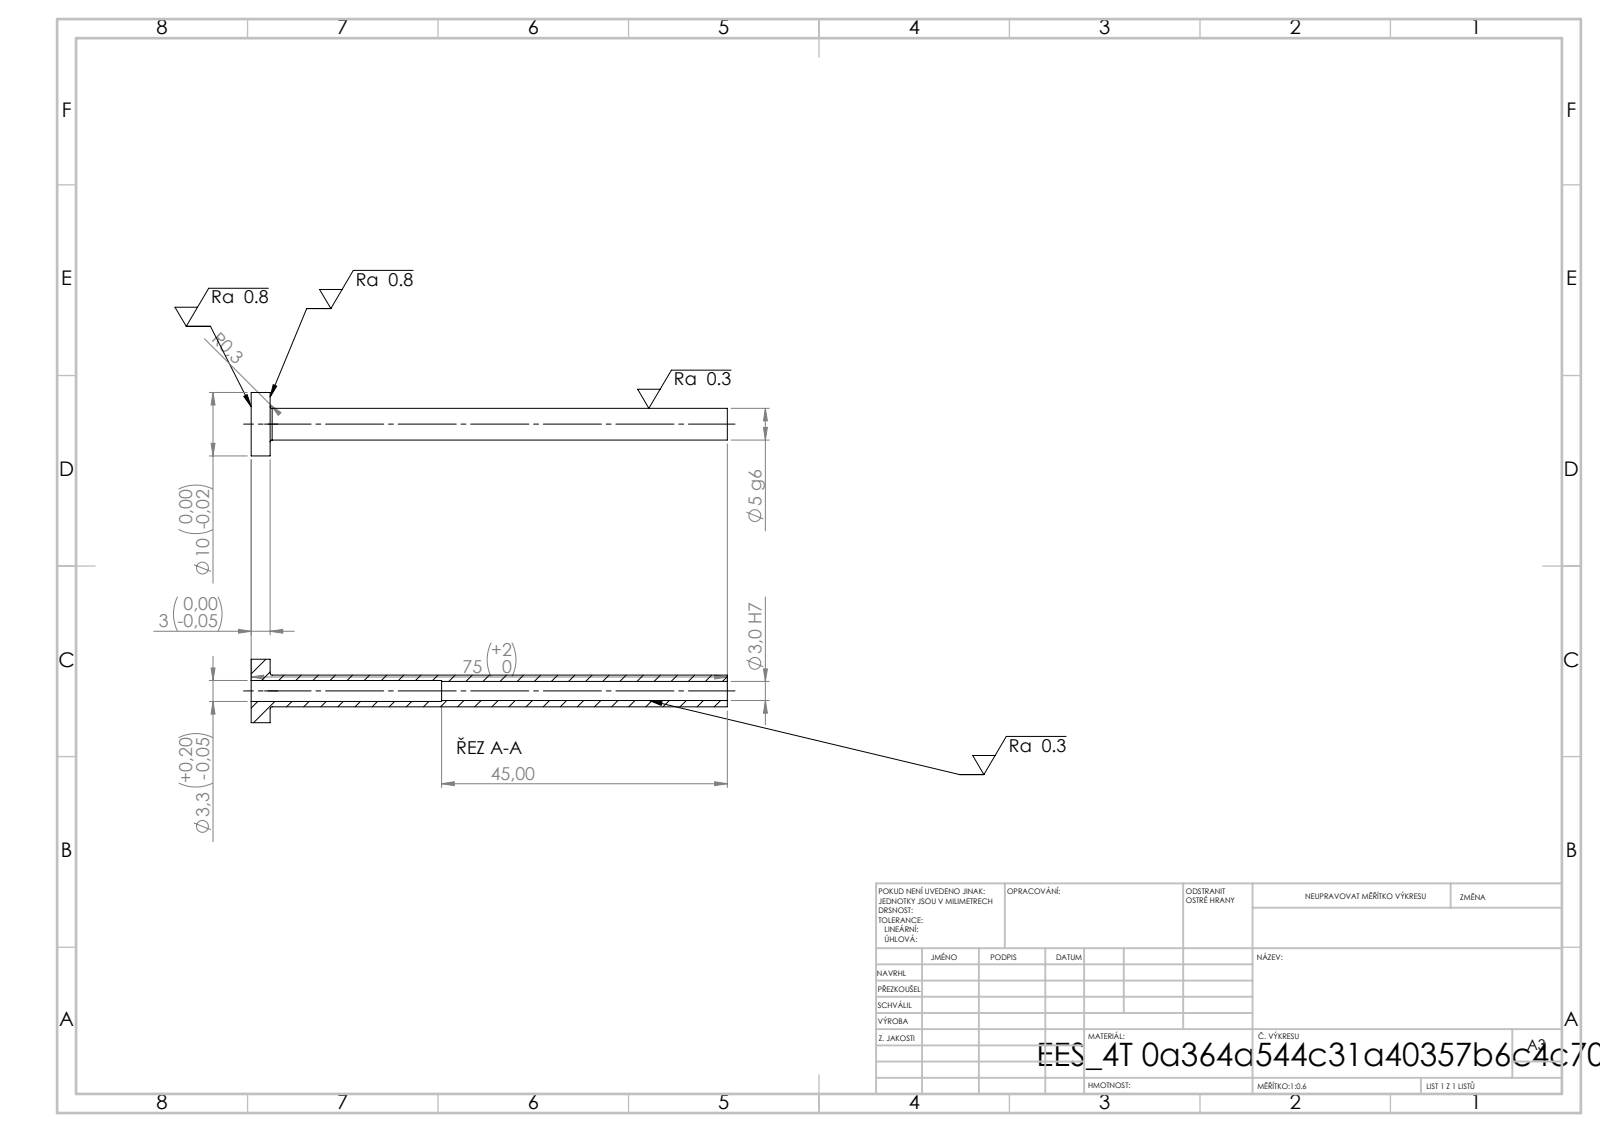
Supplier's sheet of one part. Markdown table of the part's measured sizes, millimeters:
| quantity | value |
| --- | --- |
| STEP written by | SolidWorks 2019 (CONFIG_CONTROL_DESIGN) |
| units | millimeters |
| bodies | 1 solid, 14 faces (4 planar, 8 cylindrical, 2 other) |
| overall size | 75 × 10 × 10 |
| volume | 1 075 mm³ |
| surface area | 2 101 mm² |
| round holes (diameter × count) | 3 × 1, 3.3 × 1 |
| round bosses / shafts (diameter × count) | 10 × 1, 5 × 1 |
| main face-to-face distances | 3, 75, 72, 30, 27, 45 |
